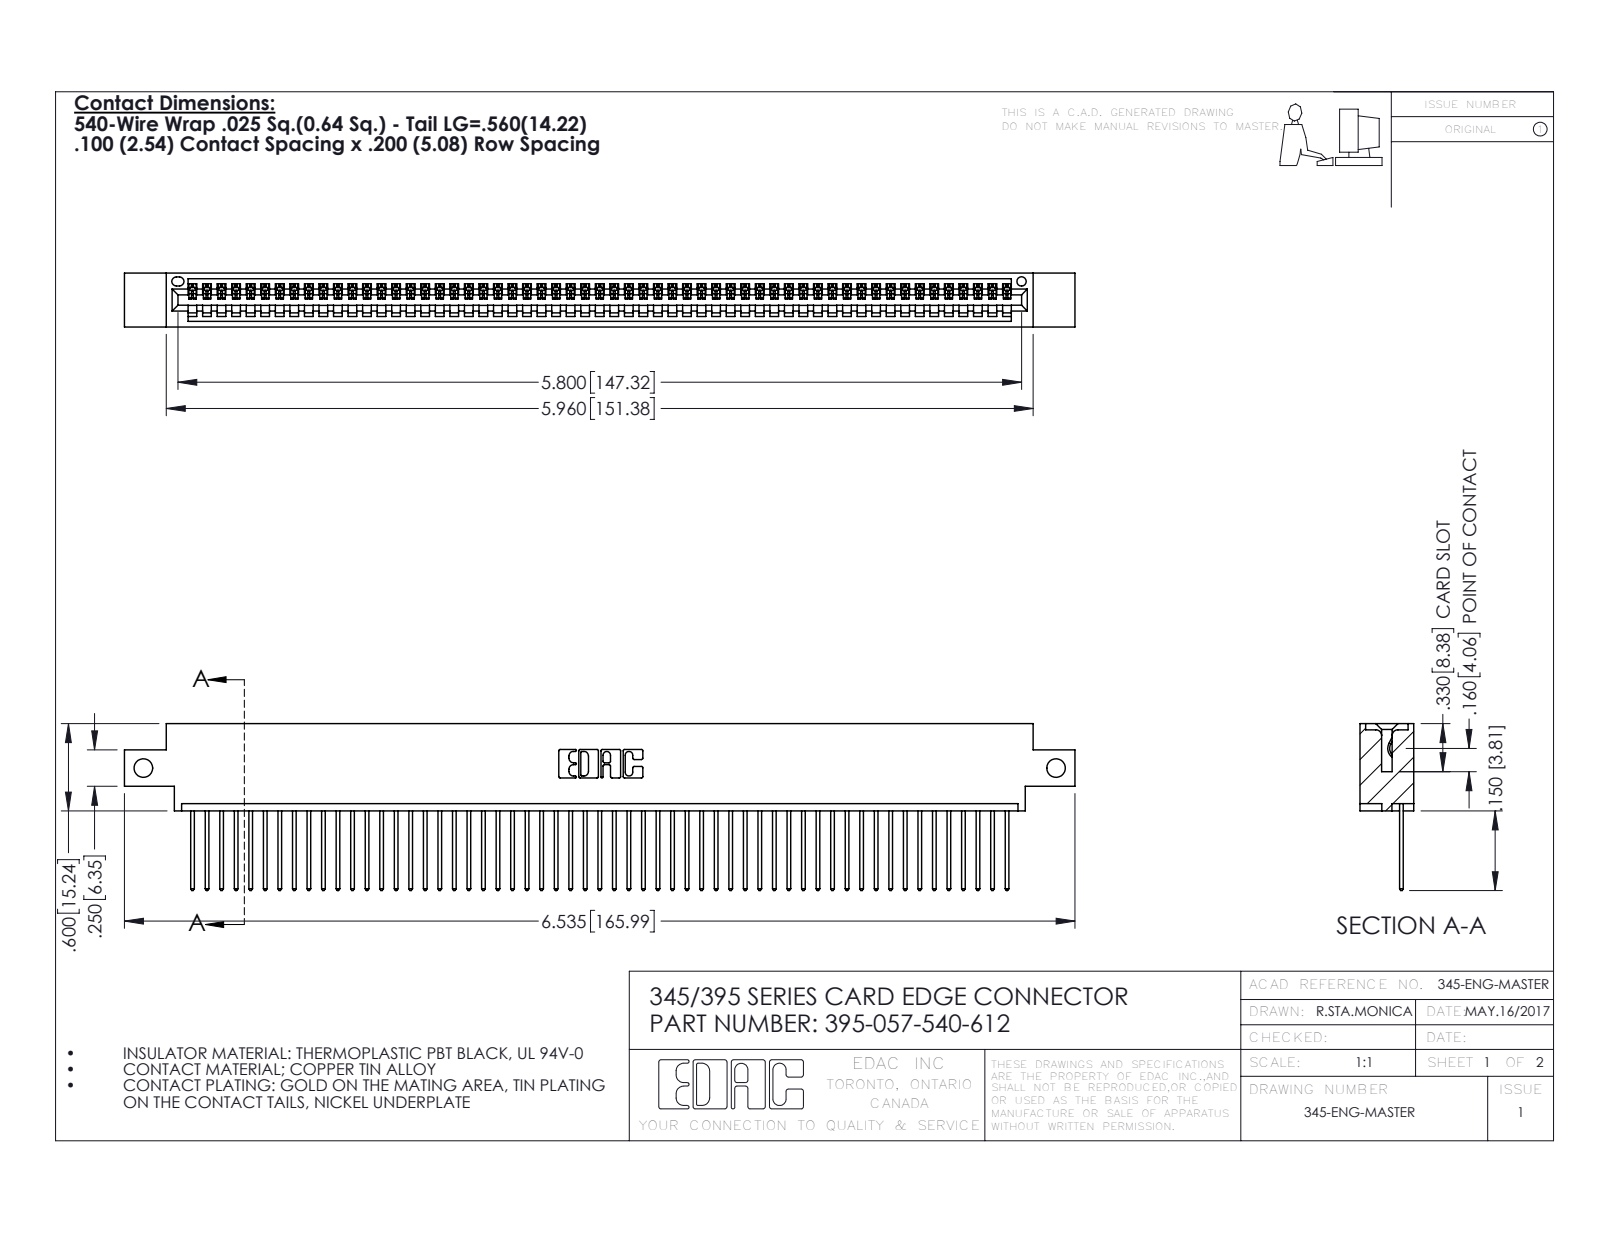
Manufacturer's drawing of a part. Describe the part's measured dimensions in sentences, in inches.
The part is named "345-292-001_345-293-140; 345 Part_0.170 Offset - Side Mount; 395-057-540-612". Its 3-D file was written by "SolidWorks 2016 (CONFIG_CONTROL_DESIGN)". It is 58 solids with 3436 faces: 2364 planar, 1072 cylindrical and 0 other. Overall it measures 6.535 by 1.147 by 0.37 inches. Its volume is 0.962 cubic inches and its surface area 33.63 square inches. Round holes: 2 of diameter 0.128, 1 of diameter 0.064. Partial cylindrical surfaces (rounded edges, fillets, slot ends): 114 of radius 0.006, 114 of radius 0.01, 22 of radius 0.01, 6 of radius 0.007, 6 of radius 0.031, 3 of radius 0.026, 2 of radius 0.031, 2 of radius 0.04. The main face-to-face distances are 0.072, 0.298, 0.37, 0.098, 0.272, 0.025, 0.2, 0.225, 0.175, 0.149. The hole center spacings are 6.275.
